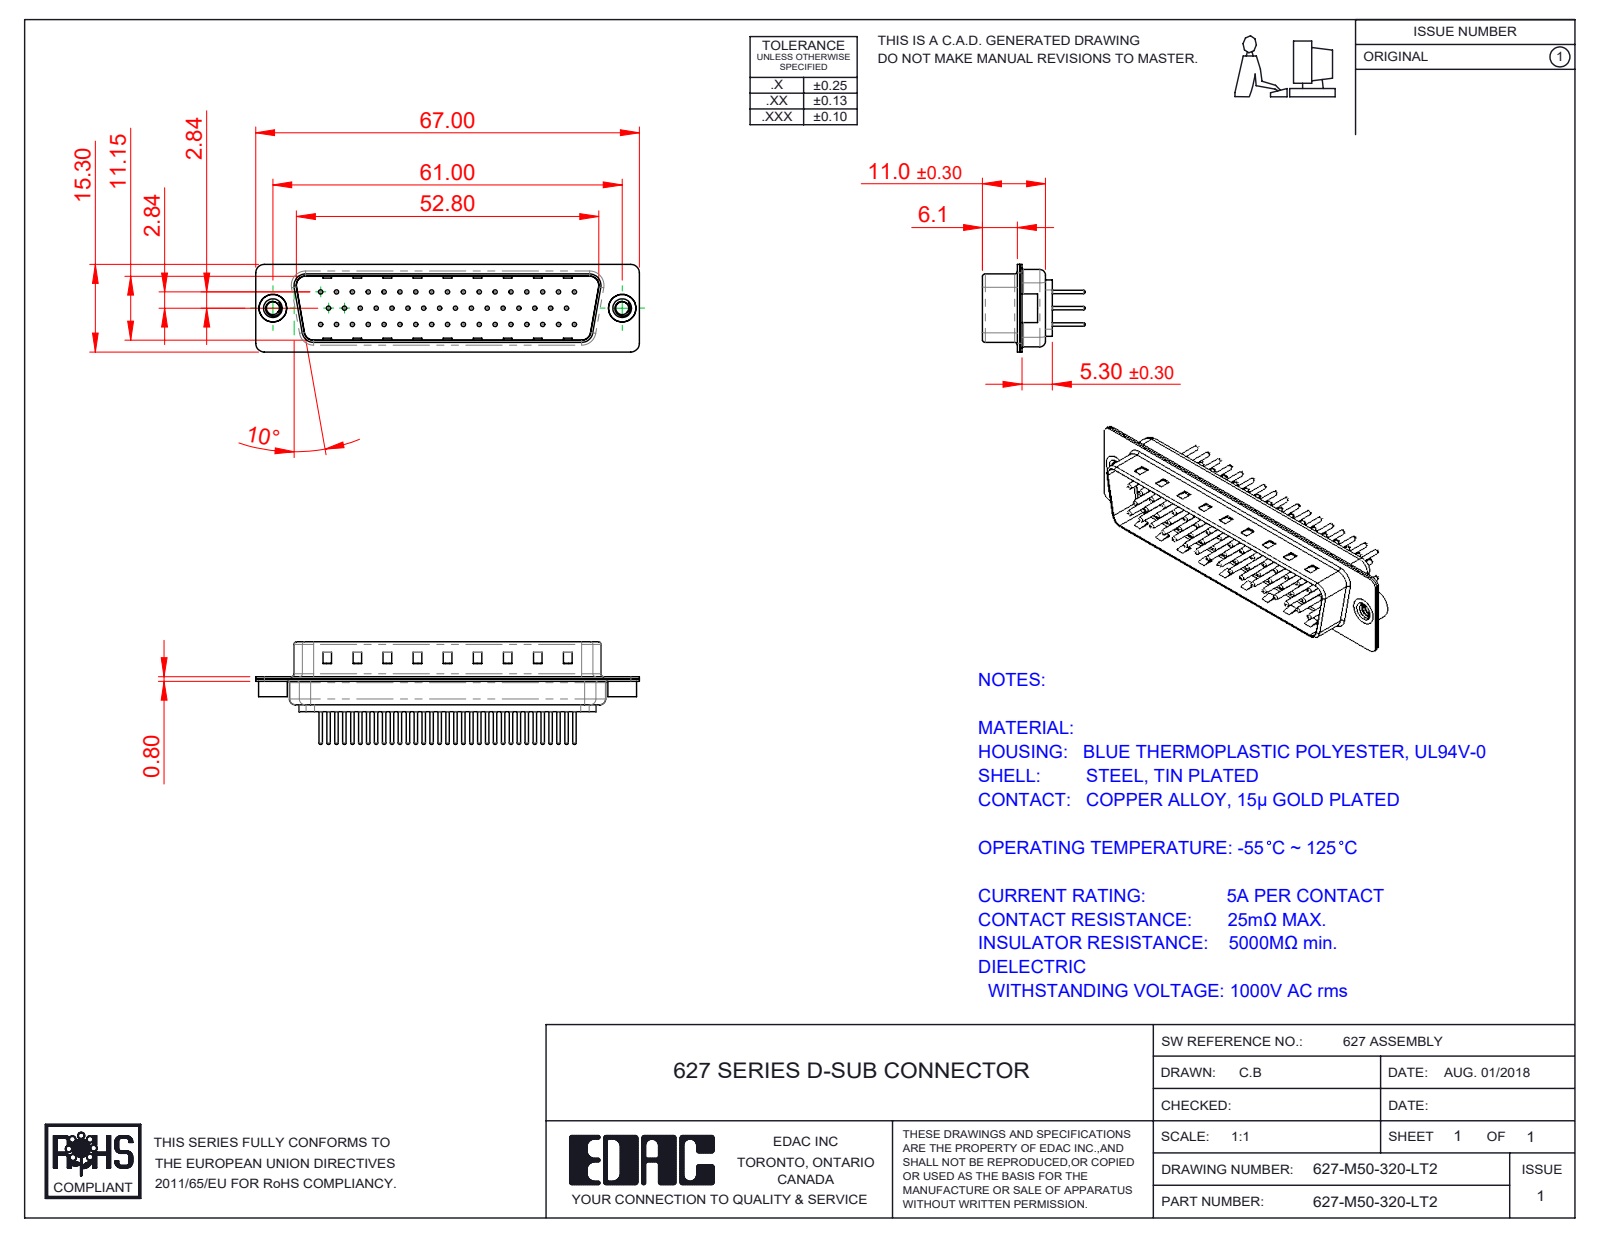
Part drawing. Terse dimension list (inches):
name: 627M 4-40 Threaded Rivet; 627M Housing_50 Contacts; 627M Shell Front_50 Contacts; 627M Contact Row 1_20 (+4 more)
written by: SolidWorks 2020 (CONFIG_CONTROL_DESIGN)
unit: in
bodies: 55 solids, 2262 faces (553 planar, 841 cylindrical, 868 other)
size: 2.638 × 0.705 × 0.602
volume: 0.276 in³; area: 16.58 in²
holes: 50× ⌀0.03, 50× ⌀0.063, 50× ⌀0.079, 2× ⌀0.089, 2× ⌀0.157, 2× ⌀0.189
bosses: 50× ⌀0.059, 50× ⌀0.024, 2× ⌀0.197, 2× ⌀0.193
rounds: 16× R0.059, 12× R0.079, 8× R0.02, 8× R0.063, 4× R0.01, 4× R0.024, 4× R0.026, 4× R0.035
face distances: 0.016, 0.455, 0.224, 0.24, 0.031, 0.03, 0.485, 0.485, 0.516, 0.209
hole spacings: 0.124, 0.109, 0.218, 0.327, 0.436, 0.545, 0.654, 0.198
